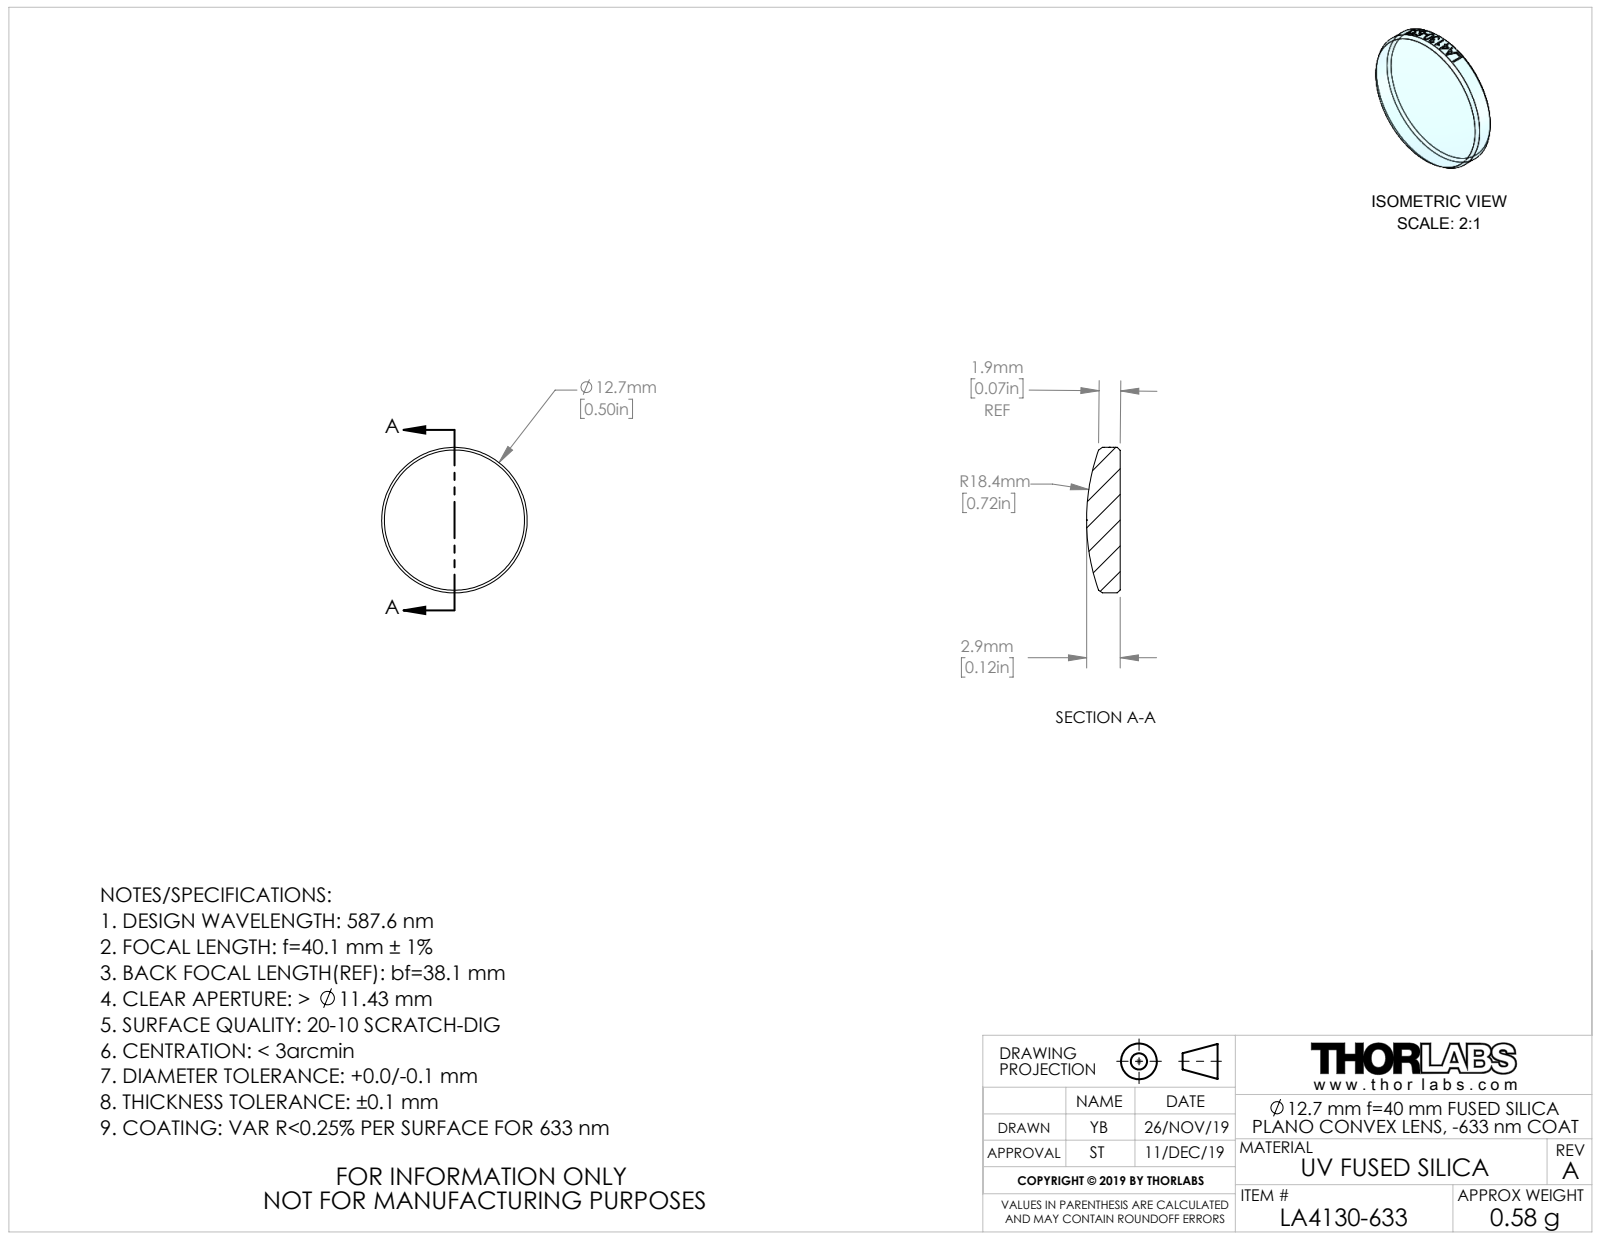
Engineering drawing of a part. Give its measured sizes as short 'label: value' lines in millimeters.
name: CTN014999-999; CTN015018
written by: SolidWorks 2018 (AUTOMOTIVE_DESIGN)
unit: mm
bodies: 1 solid, 29 faces (1 planar, 22 cylindrical, 6 other)
size: 12.7 × 12.7 × 2.93
volume: 298 mm³; area: 320 mm²
bosses: 1× ⌀12.7
